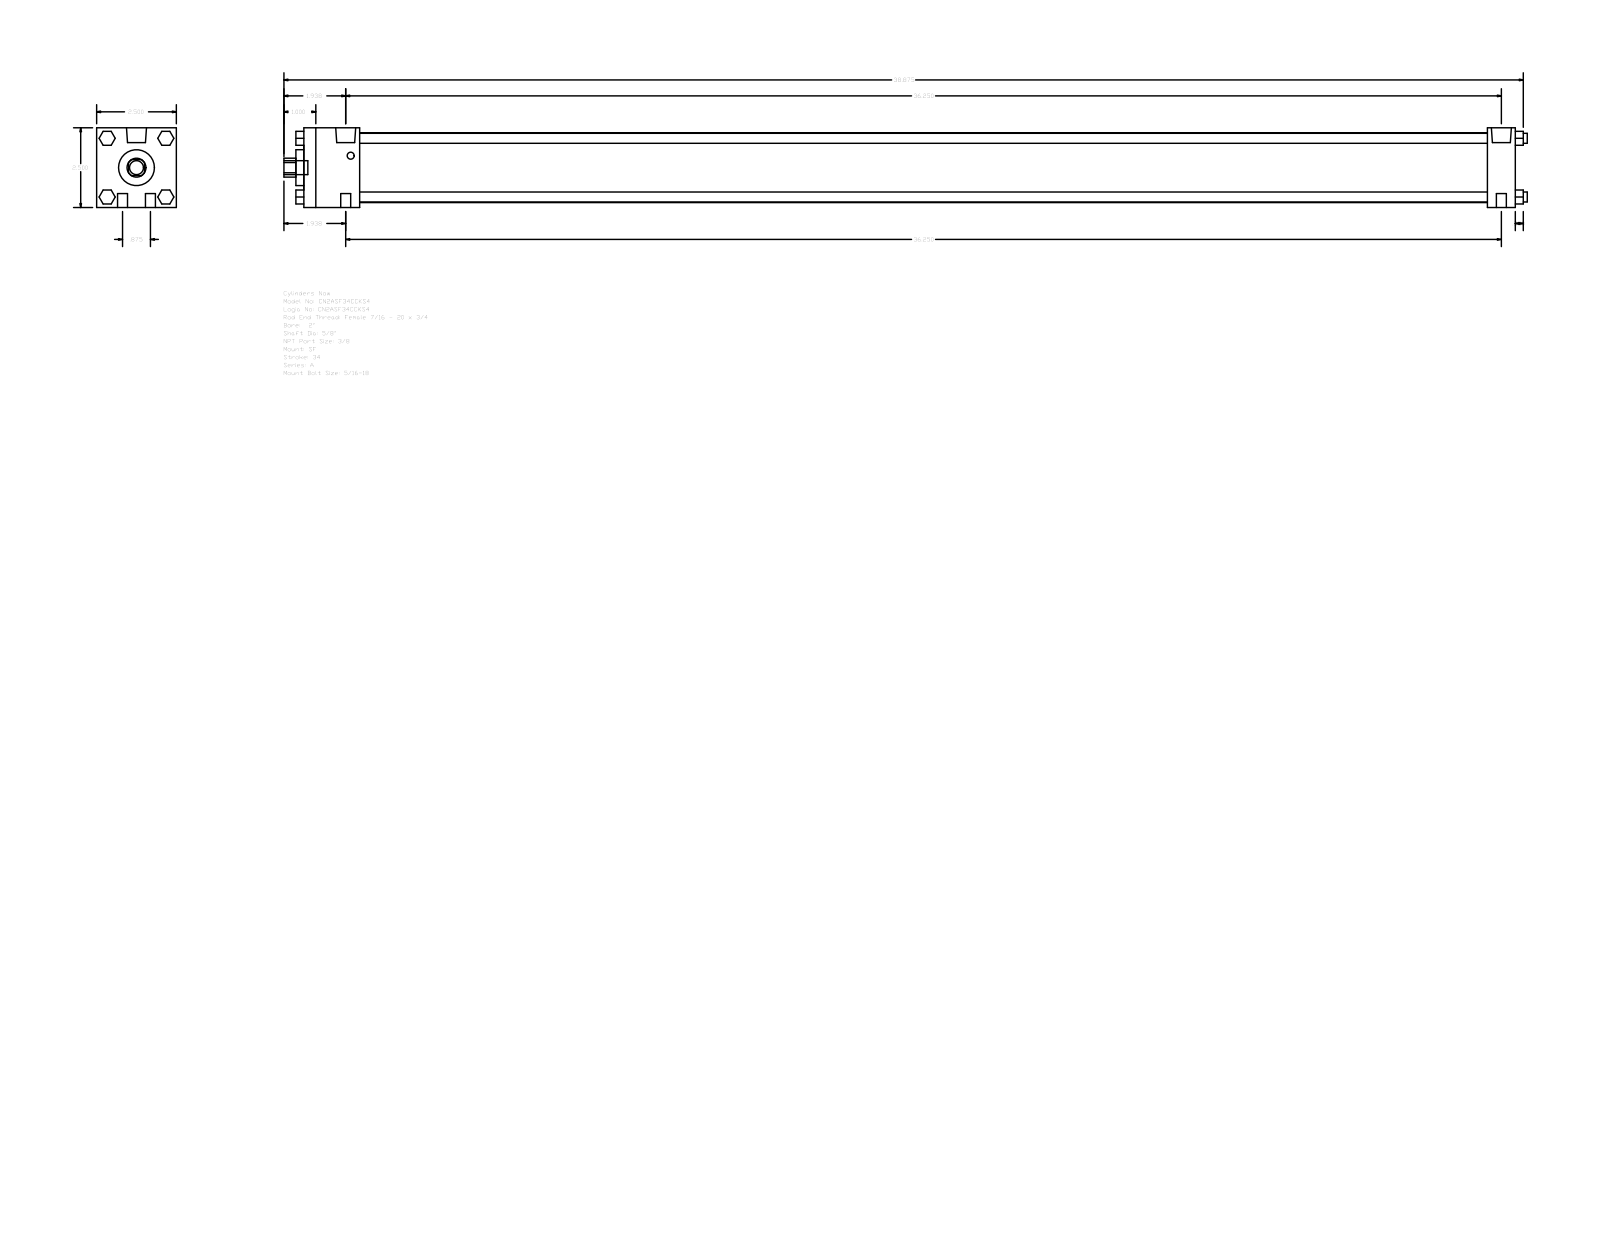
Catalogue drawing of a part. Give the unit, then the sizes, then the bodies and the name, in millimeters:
Units: millimetres
Overall size (bounding box): 990.6 × 63.5 × 63.5
Round holes (diameter × count): ⌀15.88 ×1, ⌀28.57 ×1, ⌀55.63 ×1
Round bosses / shafts (diameter × count): ⌀7.94 ×8, ⌀15.93 ×2, ⌀5.56 ×2, ⌀11.11 ×1
Partial cylindrical surfaces — rounded edges, fillets, slot ends (radius × count): R7.54 ×1
Main face-to-face distances: 63.5, 965.2, 942.97, 22.23, 44.45, 898.52, 920.75, 50.8, 971.55, 6.35
Bodies: 0 solids, 124 faces (94 planar, 30 cylindrical, 0 other)
Part name (STEP PRODUCT): A_SF__0200_0.625
STEP written by: GSSL Pune (CONFIG_CONTROL_DESIGN)
